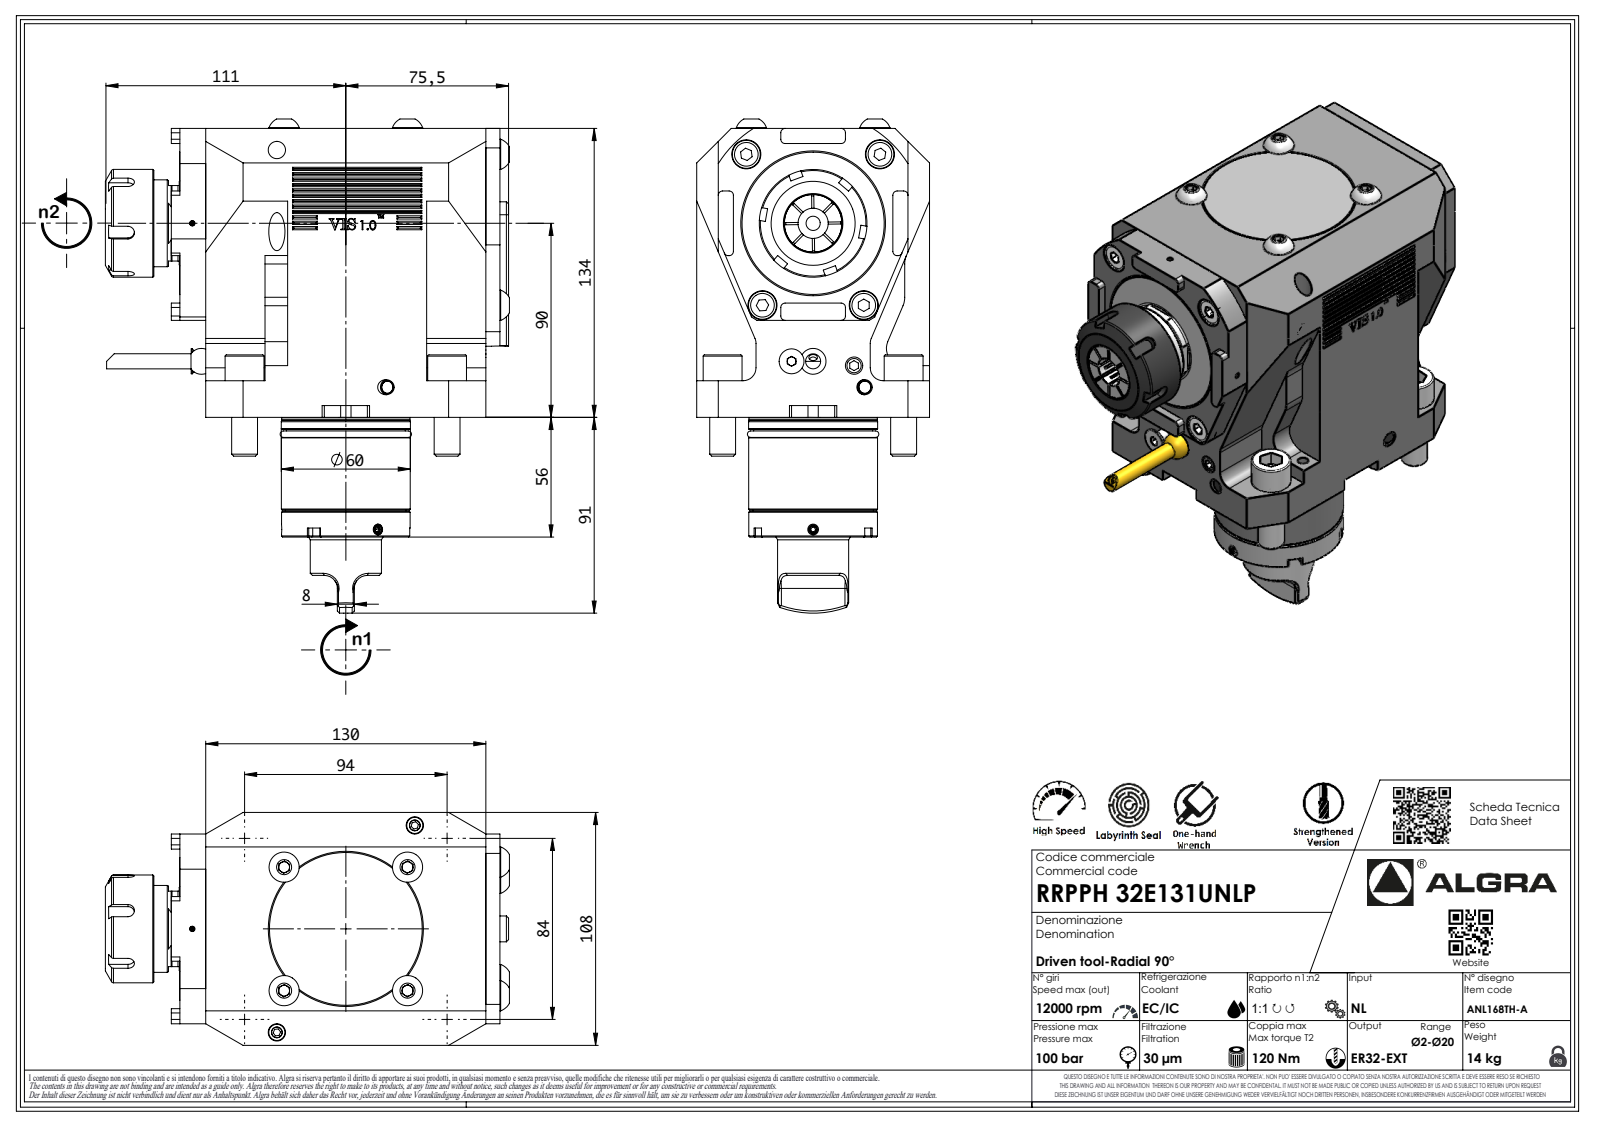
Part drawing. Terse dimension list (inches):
name: RRPPH32E131UNLP
written by: SolidWorks 2023 (AUTOMOTIVE_DESIGN)
unit: in
bodies: 1 solid, 1020 faces (680 planar, 138 cylindrical, 202 other)
size: 8.85 × 7.366 × 4.252
volume: 124.3 in³; area: 199.9 in²
holes: 1× ⌀0.083
bosses: 4× ⌀0.709, 4× ⌀0.472, 1× ⌀2.358, 1× ⌀2.354, 1× ⌀2.35, 1× ⌀2.343, 1× ⌀2.173, 1× ⌀1.969
rounds: 21× R0.008, 18× R0.315, 16× R0.079, 11× R0.236, 9× R0.118, 7× R0.013, 7× R0.02, 7× R0.146
face distances: 4.252, 5.276, 1.083, 0.472, 4.035, 0.256, 5.374, 1.496, 0.217, 5.846
